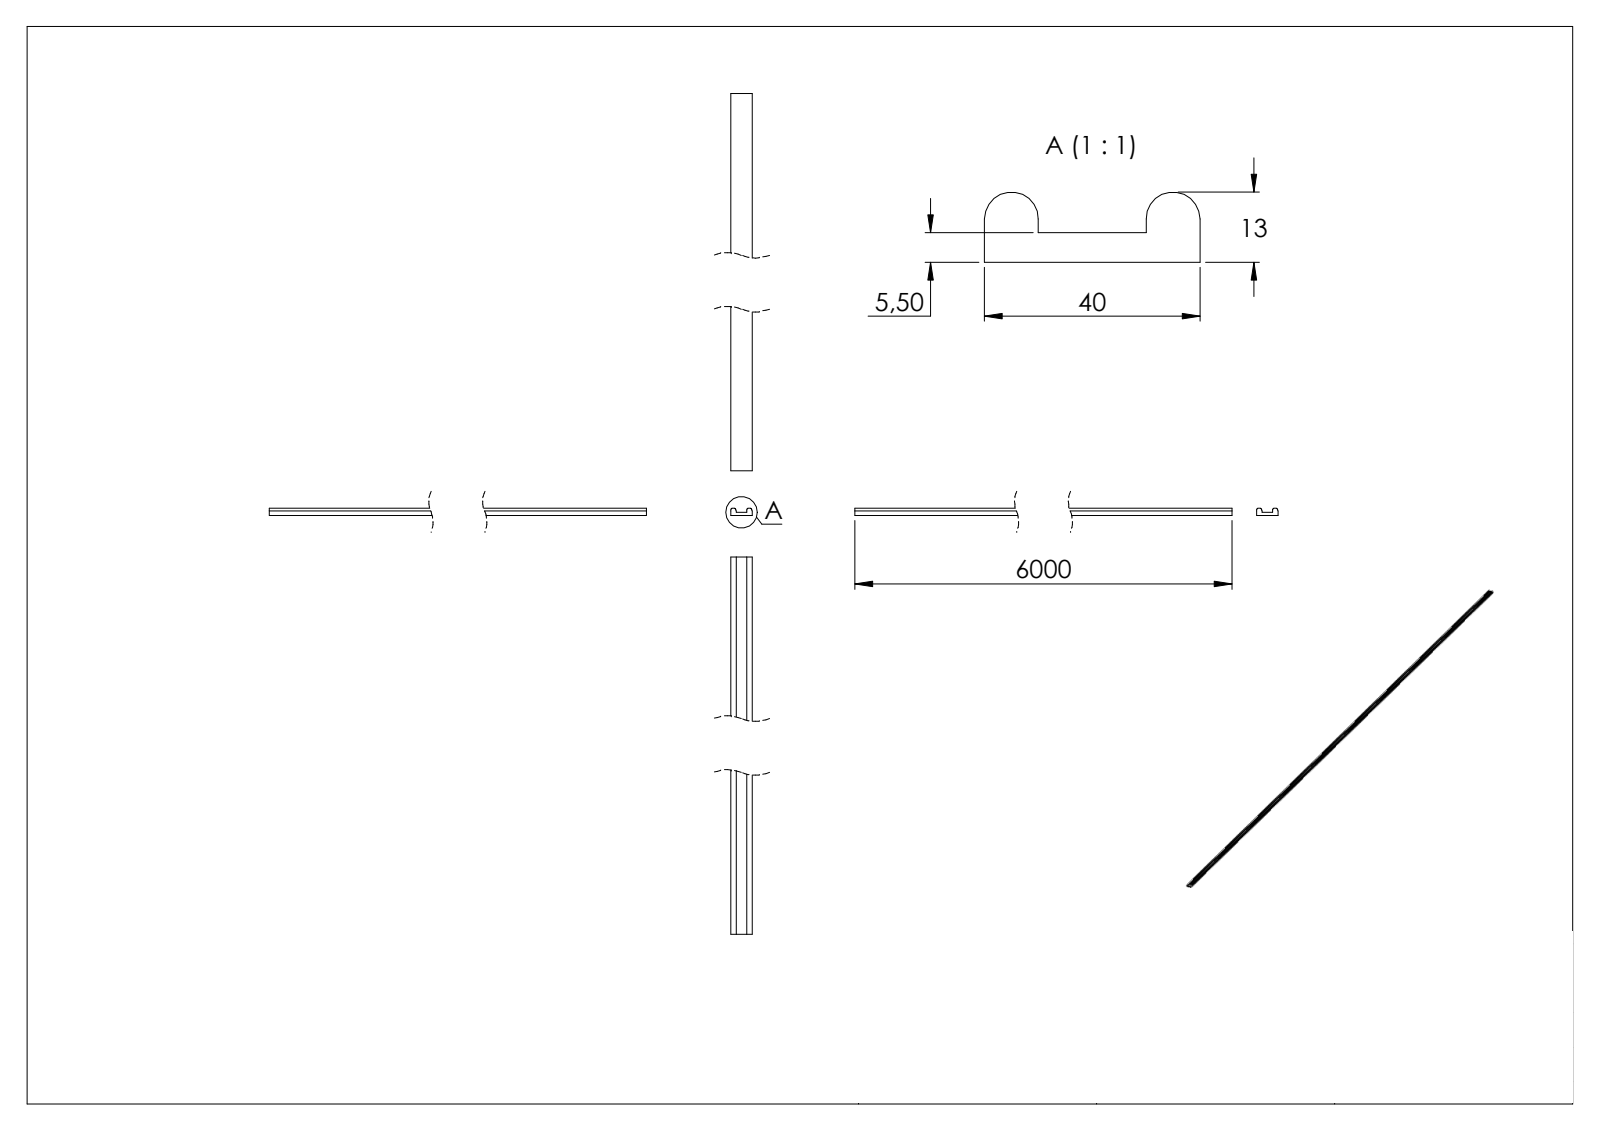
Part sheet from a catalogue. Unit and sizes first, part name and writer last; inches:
Units: inches
Overall size (bounding box): 236.22 × 1.575 × 0.512
Partial cylindrical surfaces — rounded edges, fillets, slot ends (radius × count): R0.197 ×2
Main face-to-face distances: 0.217, 1.575, 0.394, 1.181, 0.787, 236.22, 0.213, 0.129, 0.013, 118.11
Volume: 127.6 in³ · Surface area: 1 047 in²
Bodies: 1 solid, 245 faces (123 planar, 2 cylindrical, 120 other)
Part name (STEP PRODUCT): 2303-6
STEP written by: SolidWorks 2018 (CONFIG_CONTROL_DESIGN)
